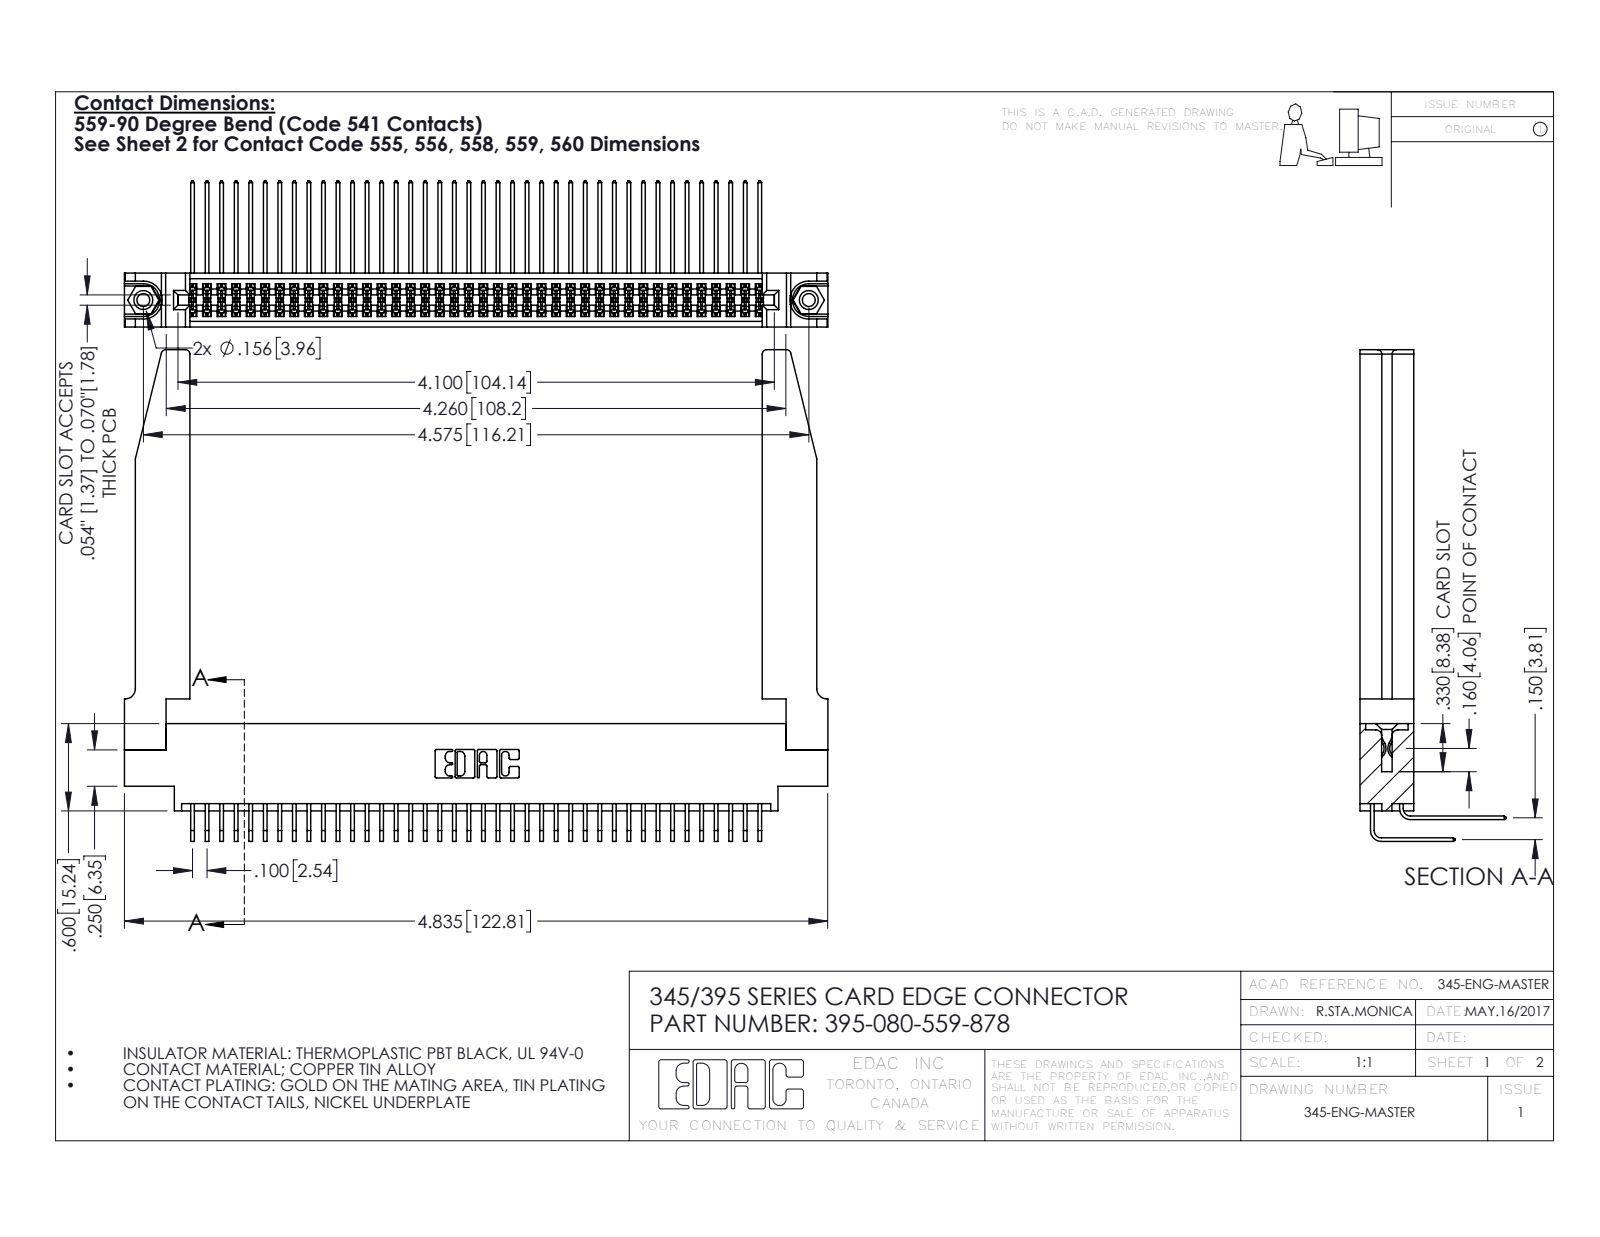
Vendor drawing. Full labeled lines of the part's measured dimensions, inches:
Part name (STEP PRODUCT): 345-292-001_559 Tail - 2; 345-250-001_345-250-001-102; 345-292-001_558 559 Tail - 1; 345-220-078_345-220-078 (+2 more)
STEP written by: SolidWorks 2016 (CONFIG_CONTROL_DESIGN)
Units: inches
Bodies: 85 solids, 4524 faces (3026 planar, 1446 cylindrical, 52 other)
Overall size (bounding box): 4.836 × 3.379 × 1.005
Volume: 1.222 in³ · Surface area: 42.22 in²
Round holes (diameter × count): ⌀0.089 ×2, ⌀0.125 ×2, ⌀0.156 ×2, ⌀0.064 ×1
Round bosses / shafts (diameter × count): ⌀0.155 ×2
Partial cylindrical surfaces — rounded edges, fillets, slot ends (radius × count): R0.006 ×120, R0.01 ×22, R0.03 ×8, R0.007 ×6, R0.031 ×6, R0.026 ×3, R0.014 ×2, R0.019 ×2
Main face-to-face distances: 0.37, 0.072, 0.298, 0.098, 0.272, 0.025, 0.2, 0.225, 0.15, 0.175
Hole centre spacings: 0.27, 4.339, 4.575
